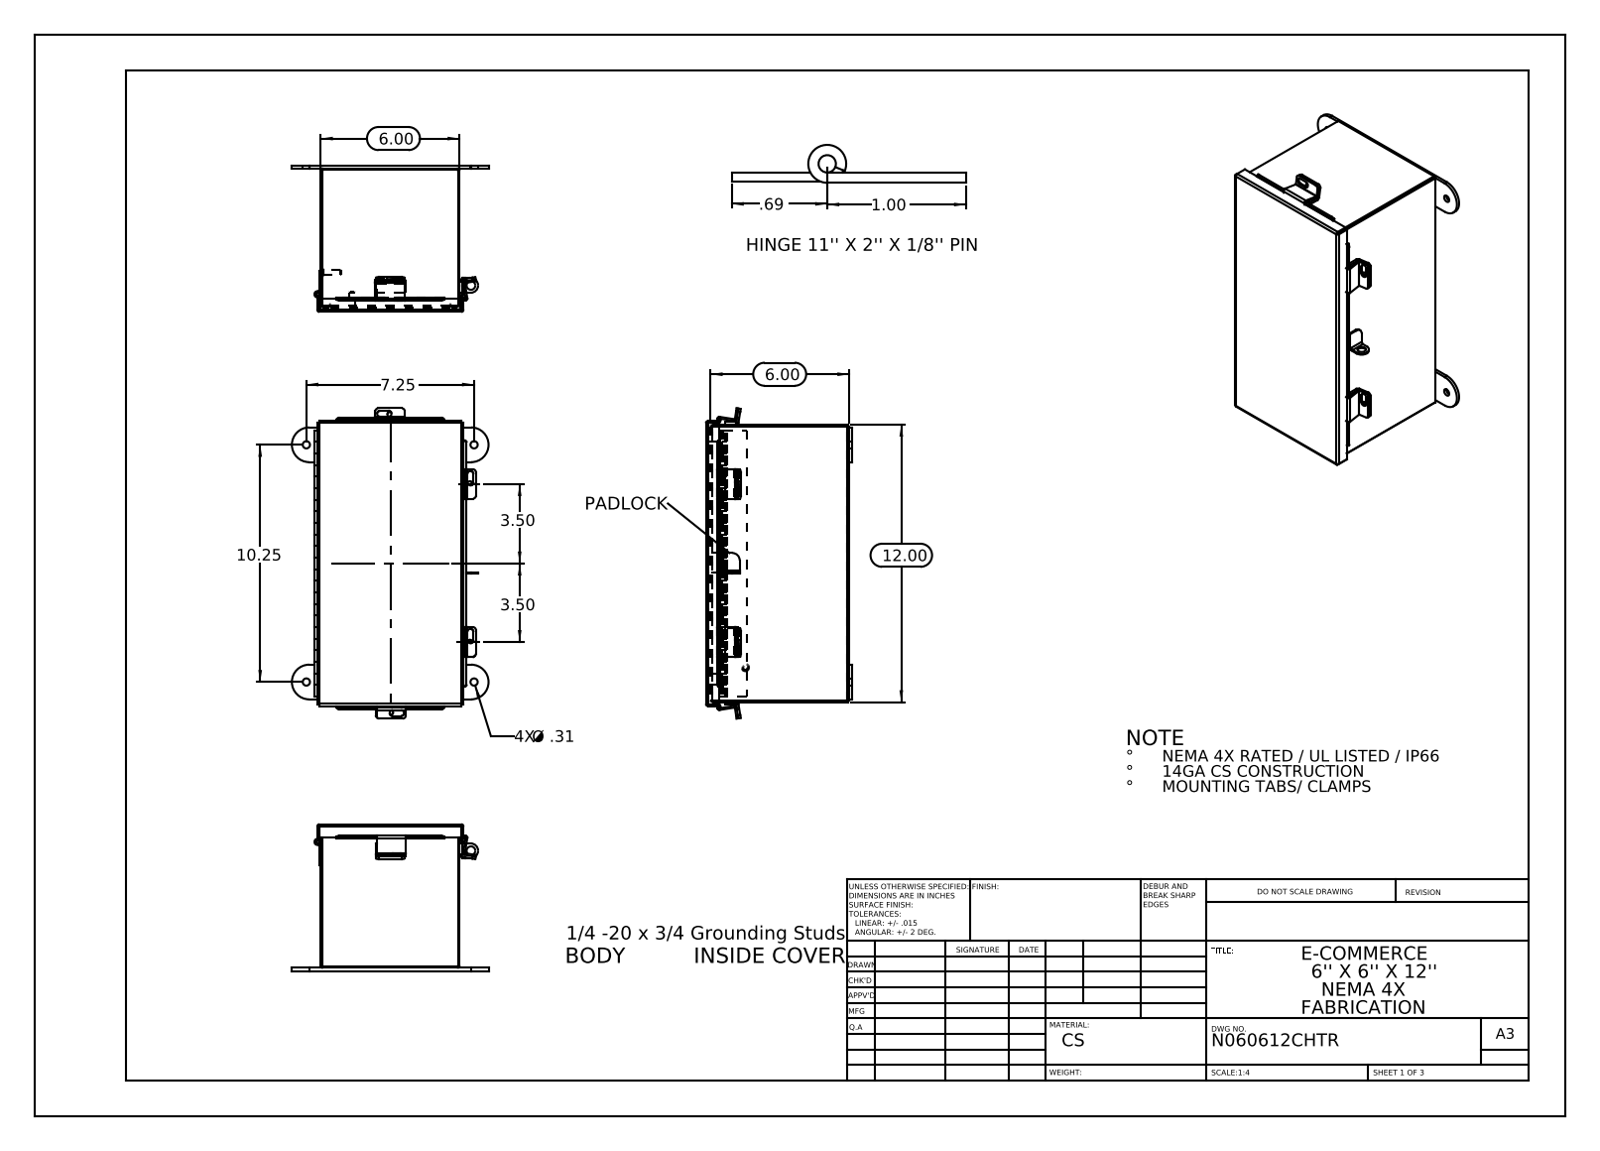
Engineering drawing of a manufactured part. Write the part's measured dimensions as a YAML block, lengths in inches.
part_name: "N060612SSCHTR _JIC Hinge; N060612SSCHTR Hinge Cover Side JIC; N060612SSCHTR Mounting Bracket; HW-CLH-JH-20154 (+8 more)"
step_written_by: "SolidWorks 2013 (AUTOMOTIVE_DESIGN)"
units: inches
bodies: {solids: 19, faces: 636, planar: 401, cylindrical: 215, other: 20}
overall_size: [13.407, 8.5, 6.337]
volume: 35.07
surface_area: 926.1
round_holes:
  - {diameter: 0.25, count: 4}
  - {diameter: 0.313, count: 4}
  - {diameter: 0.125, count: 1}
  - {diameter: 0.125, count: 1}
  - {diameter: 0.375, count: 1}
round_bosses_or_shafts:
  - {diameter: 0.315, count: 2}
  - {diameter: 0.236, count: 2}
  - {diameter: 0.273, count: 1}
  - {diameter: 0.25, count: 1}
partial_cylinders:
  - {radius: 0.125, count: 14}
  - {radius: 0.009, count: 12}
  - {radius: 0.013, count: 10}
  - {radius: 0.088, count: 10}
  - {radius: 0.133, count: 8}
  - {radius: 0.083, count: 6}
  - {radius: 0.1, count: 6}
  - {radius: 0.75, count: 4}
face_to_face_distances: [0.075, 5.925, 6.128, 6, 5.85, 6.203, 6.053, 11.925, 11.85, 12]
hole_center_spacings: [7.25, 10.25, 12.555, 6.637, 6.85]
